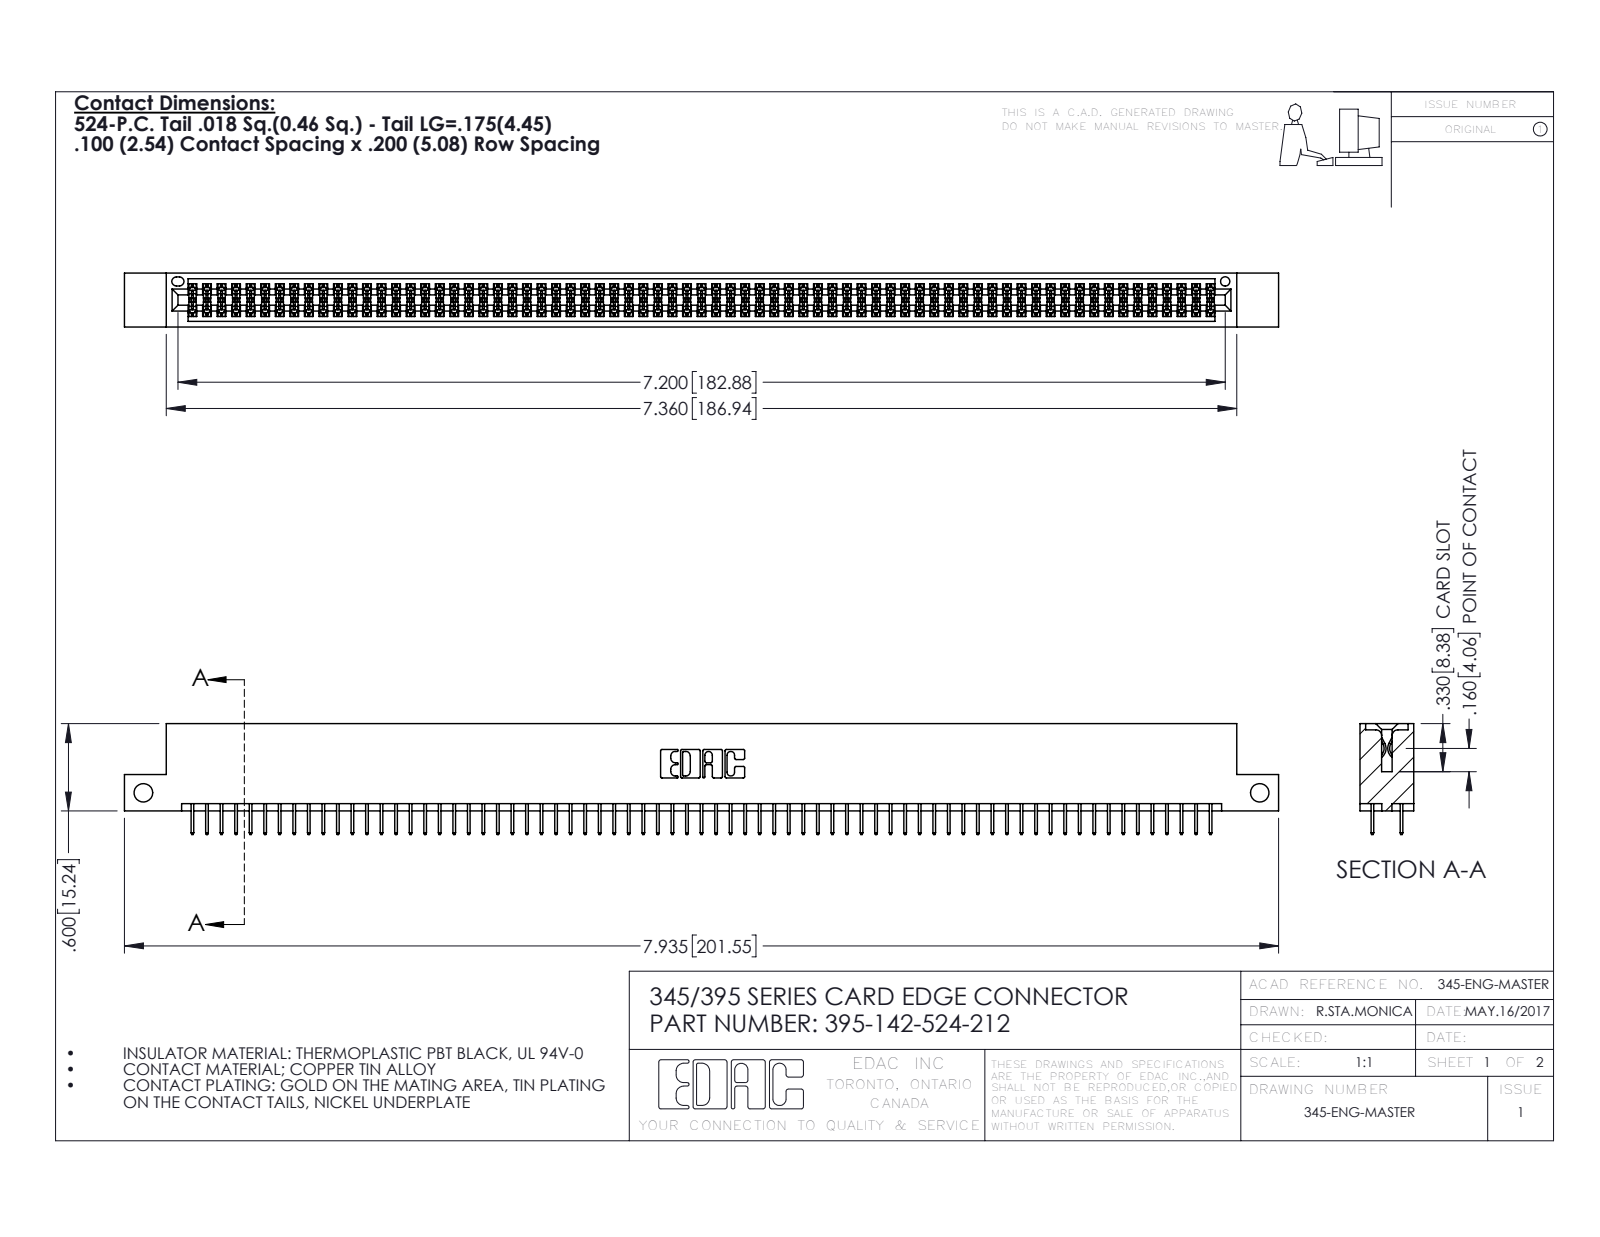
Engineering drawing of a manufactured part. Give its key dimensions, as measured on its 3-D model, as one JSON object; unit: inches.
{"part_name": "345-292-001_345-293-124; 345 Part_Flush Mounting Lugs - Side Mount; 395-142-524-212", "step_written_by": "SolidWorks 2016 (CONFIG_CONTROL_DESIGN)", "units": "inches", "bodies": {"solids": 143, "faces": 7794, "planar": 5618, "cylindrical": 2176, "other": 0}, "overall_size": [7.935, 0.762, 0.37], "volume_in3": 1.193, "surface_area_in2": 44.56, "round_holes": [[0.128, 2], [0.064, 1]], "partial_cylinders_radius": [[0.006, 213], [0.01, 22], [0.007, 6], [0.031, 6], [0.026, 3], [0.014, 2], [0.019, 2], [0.022, 2]], "face_to_face_distances": [0.072, 0.298, 0.2, 0.37, 0.098, 0.272, 0.025, 0.225, 0.072, 0.175], "hole_center_spacings": [7.675]}
